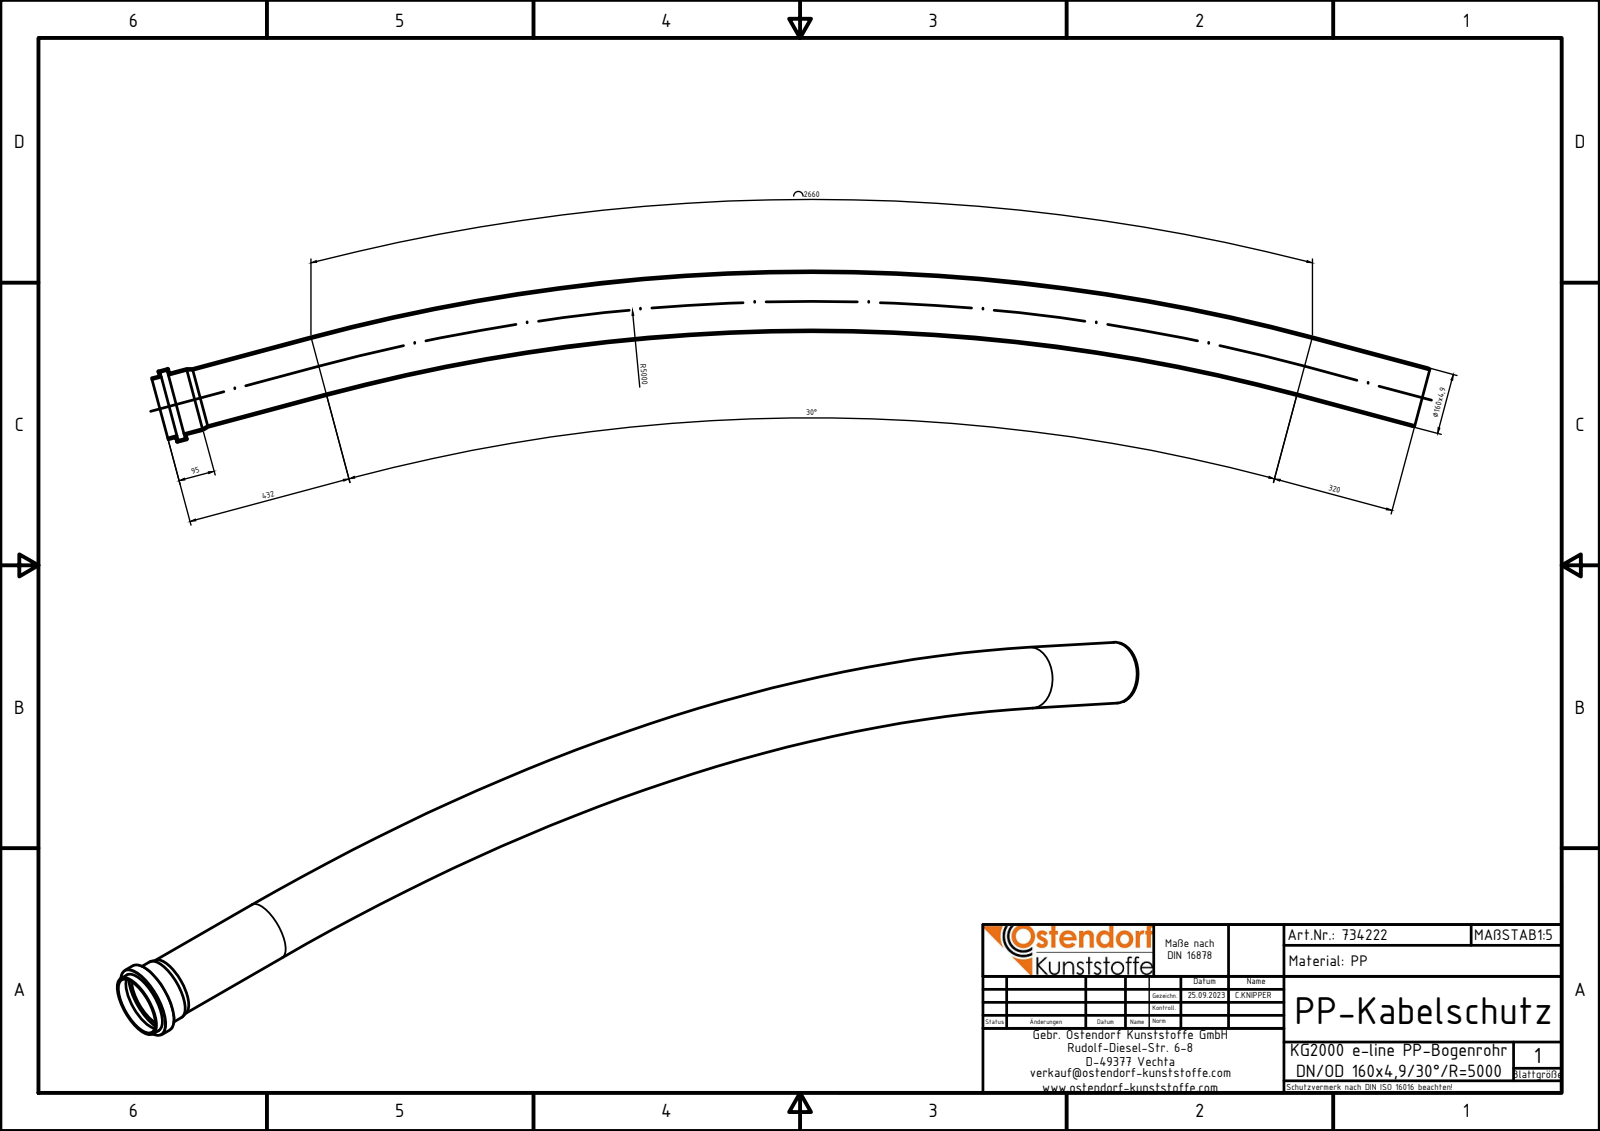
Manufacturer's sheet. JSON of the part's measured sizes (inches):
{"part_name": "734222z", "step_written_by": "Autodesk Inventor 2024 (AUTOMOTIVE_DESIGN)", "units": "inches", "bodies": {"solids": 1, "faces": 23, "planar": 6, "cylindrical": 10, "other": 7}, "overall_size": [132.154, 17.736, 7.657], "volume_in3": 496.7, "surface_area_in2": 5155, "round_holes": [[5.913, 2], [6.24, 2], [7.272, 1]], "round_bosses_or_shafts": [[6.626, 2], [6.299, 2], [7.657, 1]], "face_to_face_distances": [0.193, 0.949, 0.756, 1.142, 0.787, 0.98, 1.737, 1.93]}
